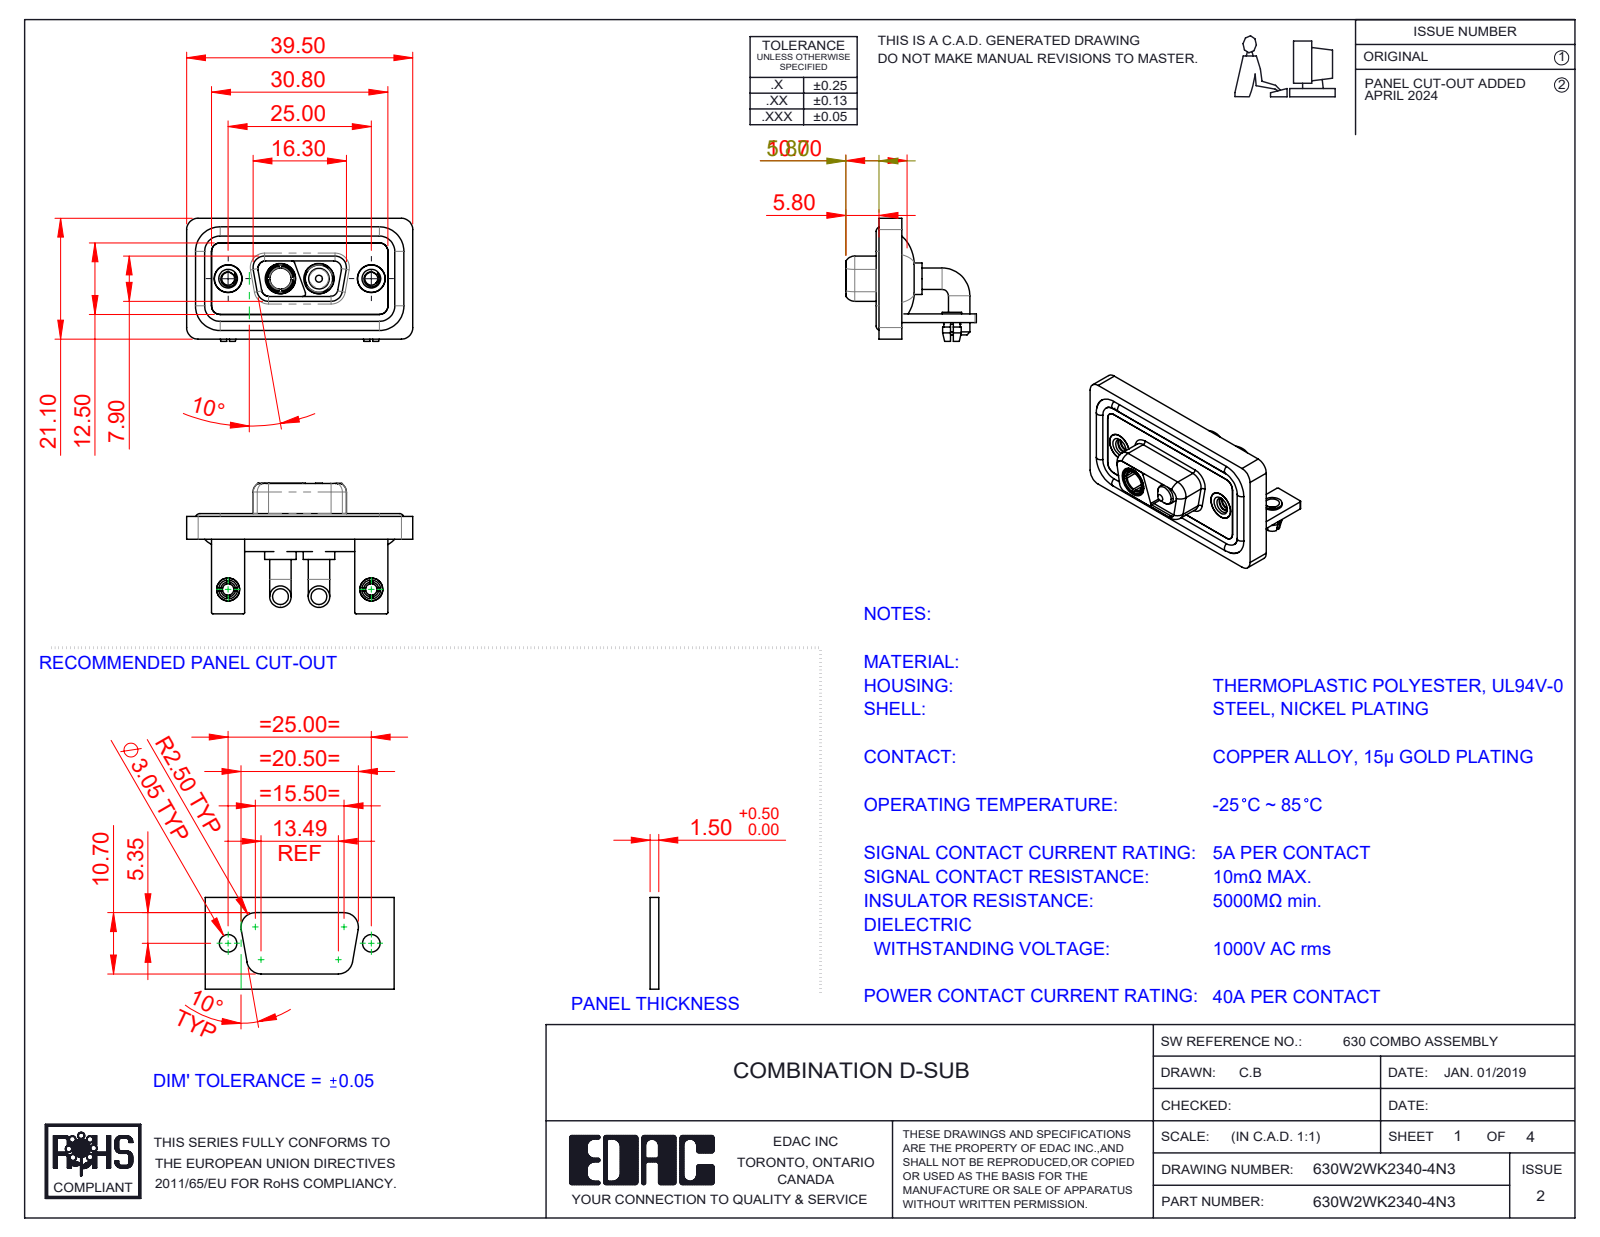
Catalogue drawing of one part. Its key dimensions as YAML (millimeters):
part_name: "630Combo Shell Rear_09 Contacts; 630Combo Shell Front_09 Contacts; 630Combo Threaded Rivet_2; Power Socket_40A RA (+6 more)"
step_written_by: "SolidWorks 2023 (CONFIG_CONTROL_DESIGN)"
units: millimeters
bodies: {solids: 15, faces: 648, planar: 212, cylindrical: 291, other: 145}
overall_size: [39.5, 22.8, 21.5]
volume: 5255
surface_area: 8528
round_holes:
  - {diameter: 4.85, count: 4}
  - {diameter: 2, count: 2}
  - {diameter: 2.26, count: 2}
  - {diameter: 2.5, count: 2}
  - {diameter: 3.2, count: 2}
  - {diameter: 4, count: 2}
  - {diameter: 4.05, count: 2}
  - {diameter: 5, count: 2}
  - {diameter: 5.3, count: 2}
  - {diameter: 3.7, count: 1}
round_bosses_or_shafts:
  - {diameter: 3.75, count: 4}
  - {diameter: 1.6, count: 4}
  - {diameter: 5.5, count: 2}
  - {diameter: 5.2, count: 2}
  - {diameter: 4.95, count: 2}
  - {diameter: 4.8, count: 2}
  - {diameter: 4.75, count: 2}
  - {diameter: 4, count: 2}
partial_cylinders:
  - {radius: 2, count: 19}
  - {radius: 1.5, count: 18}
  - {radius: 0.25, count: 16}
  - {radius: 1.35, count: 8}
  - {radius: 1.6, count: 8}
  - {radius: 0.5, count: 7}
  - {radius: 0.6, count: 4}
  - {radius: 0.65, count: 4}
face_to_face_distances: [0.4, 2.9, 1.5, 1.1, 3.7, 1.8, 0.8, 2.5, 1.6, 3.1]
hole_center_spacings: [9.14, 15.86, 25, 6.72]
